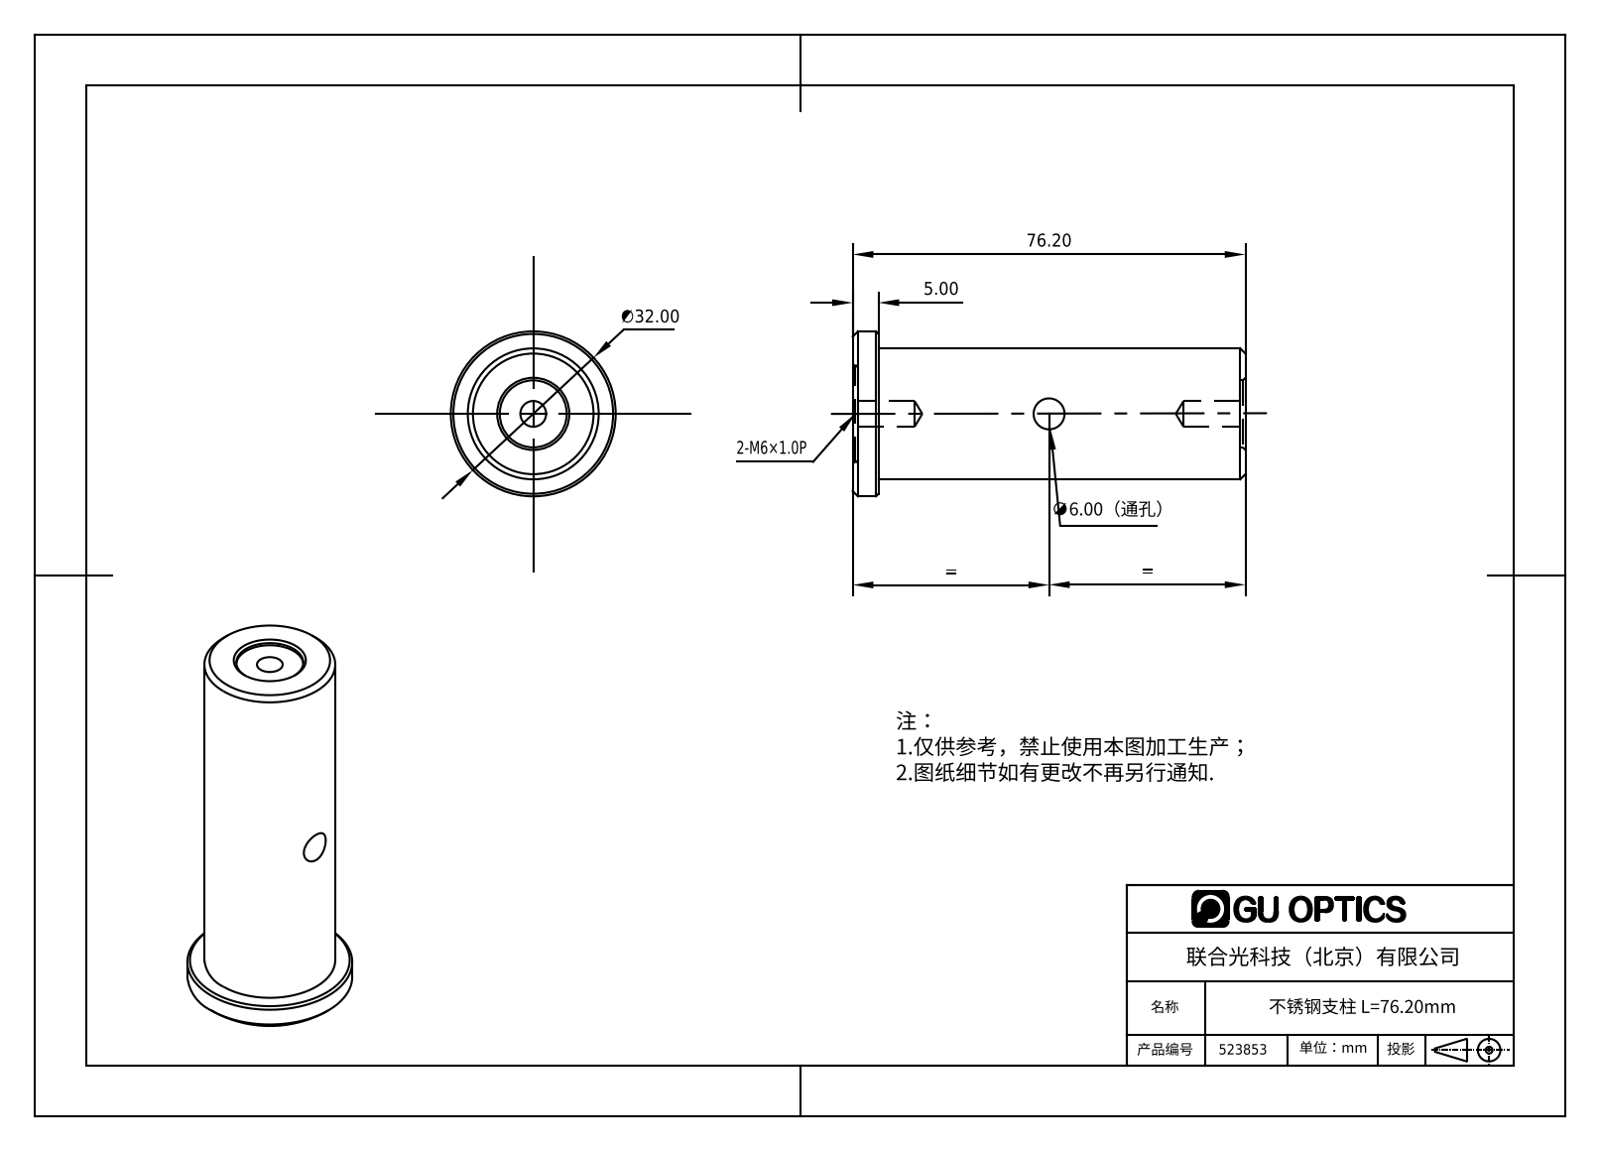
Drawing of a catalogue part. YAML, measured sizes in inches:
part_name: "523853"
step_written_by: "SolidWorks 2016 (AUTOMOTIVE_DESIGN)"
units: inches
bodies: {solids: 1, faces: 33, planar: 5, cylindrical: 14, other: 14}
overall_size: [3, 1.26, 1.26]
volume: 2.344
surface_area: 13.16
round_holes:
  - {diameter: 0.197, count: 1}
  - {diameter: 0.236, count: 1}
  - {diameter: 0.512, count: 1}
  - {diameter: 0.748, count: 1}
round_bosses_or_shafts:
  - {diameter: 1.26, count: 1}
  - {diameter: 1, count: 1}
face_to_face_distances: [0.039, 2.961, 3, 0.197, 2.803, 0.157, 2.921, 2.764]
